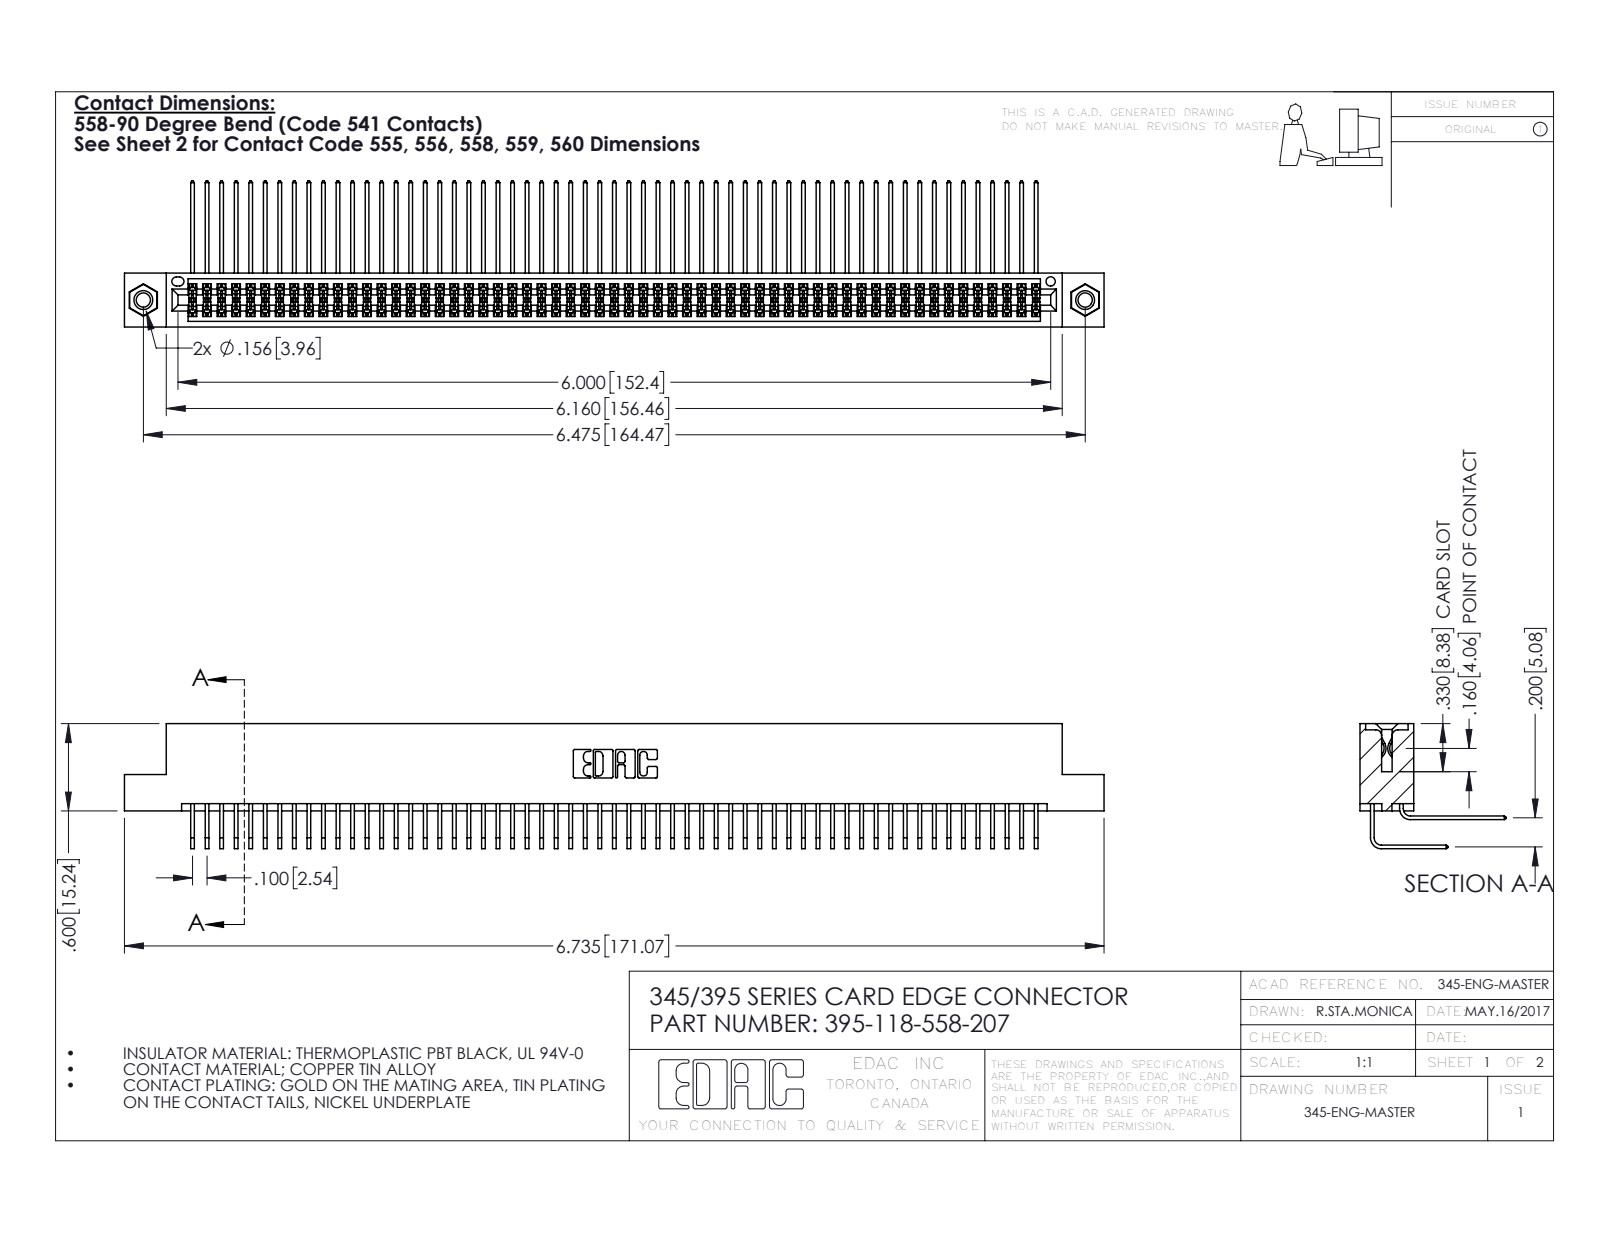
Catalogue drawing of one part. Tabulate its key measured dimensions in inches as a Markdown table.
| quantity | value |
| --- | --- |
| part name | 345 Part_Flush Mounting Lugs - 0.156 Dia-TI; 345-292-001_558 Tail - 2; 345-292-001_558 559 Tail - 1; 345-250-001_345-250-005-103 (+1 more) |
| STEP written by | SolidWorks 2016 (CONFIG_CONTROL_DESIGN) |
| units | inches |
| bodies | 121 solids, 6322 faces (4242 planar, 2064 cylindrical, 16 other) |
| overall size | 6.735 × 1.005 × 0.859 |
| volume | 1.064 in³ |
| surface area | 45.48 in² |
| round holes (diameter × count) | 0.098 × 2, 0.125 × 2, 0.156 × 2, 0.064 × 1 |
| round bosses / shafts (diameter × count) | 0.155 × 2 |
| partial cylindrical surfaces (radius × count) | 0.006 × 178, 0.01 × 22, 0.007 × 6, 0.031 × 6, 0.026 × 3, 0.014 × 2, 0.019 × 2, 0.022 × 2 |
| main face-to-face distances | 0.072, 0.298, 0.2, 0.37, 0.098, 0.272, 0.025, 0.225, 0.025, 0.175 |
| hole center spacings | 0.27, 6.239, 6.475 |
